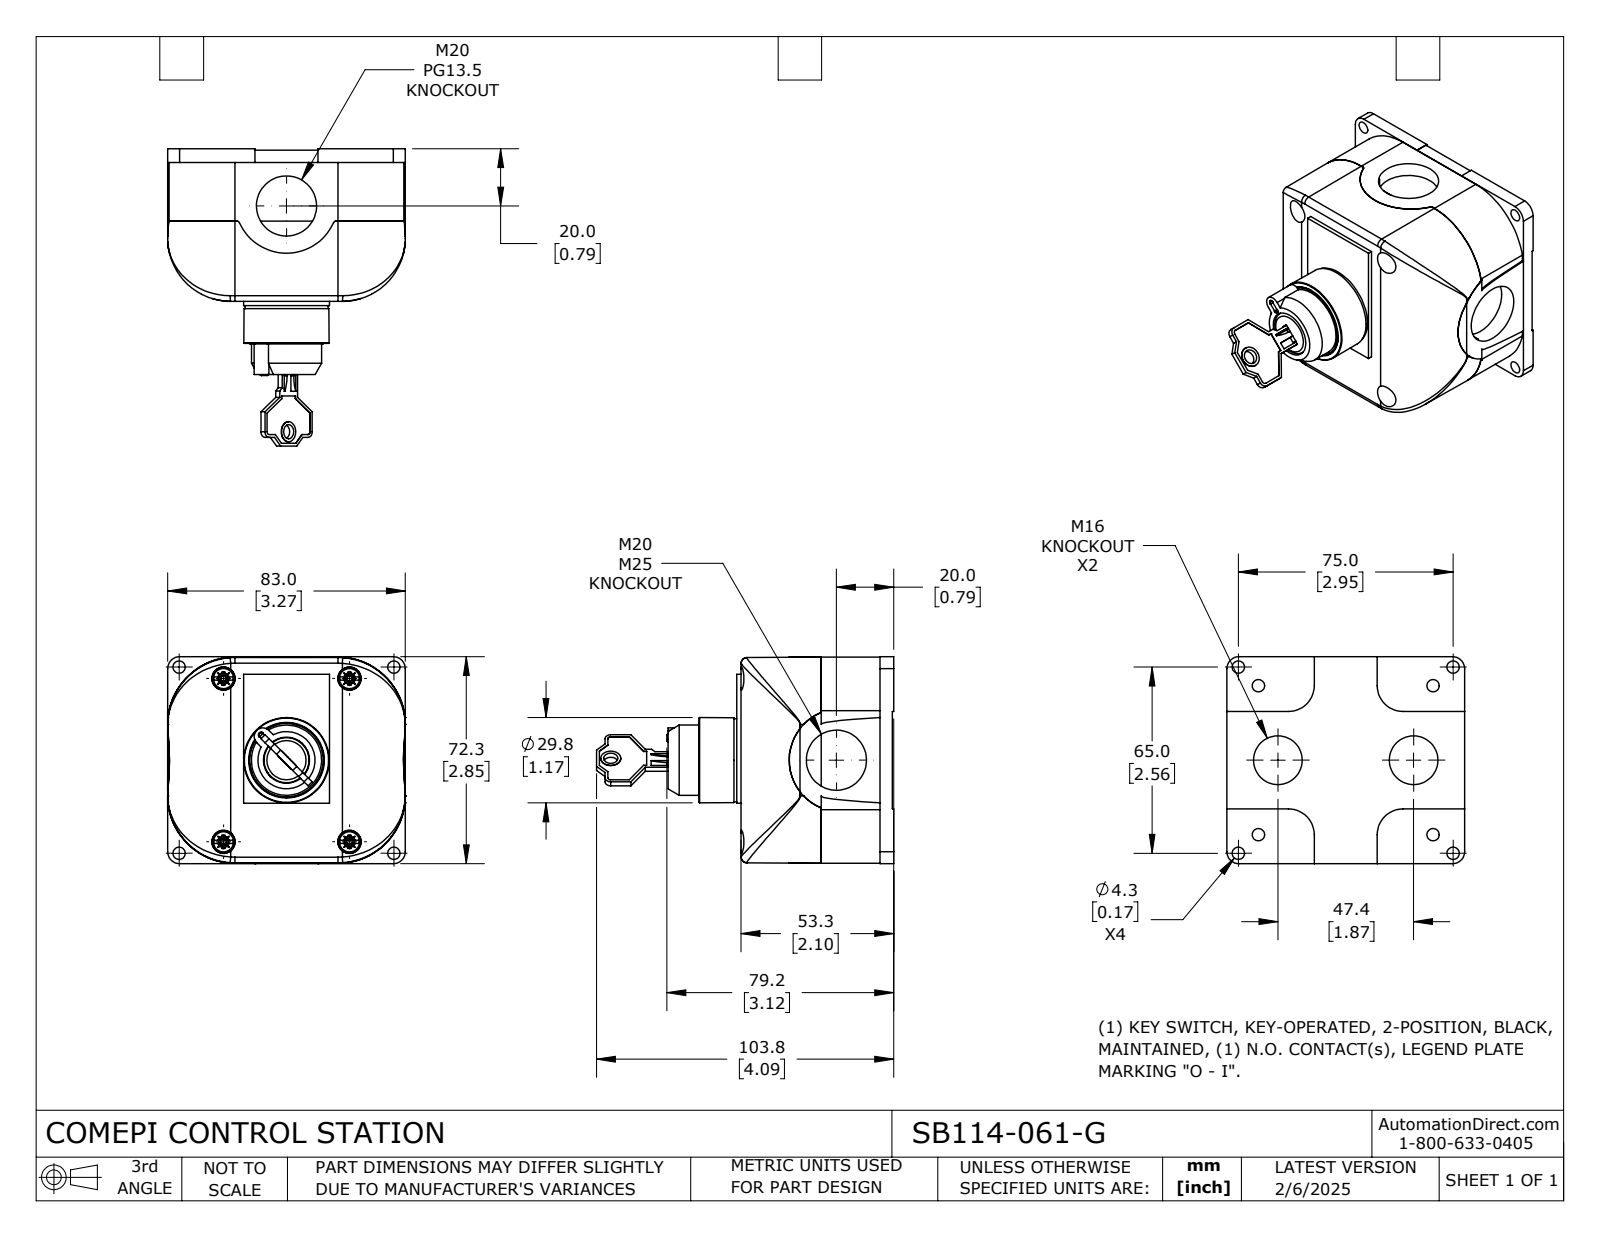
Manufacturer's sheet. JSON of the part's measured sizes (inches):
{"part_name": "SB114-061-G", "step_written_by": "SolidWorks 2024 (CONFIG_CONTROL_DESIGN)", "units": "inches", "bodies": {"solids": 5, "faces": 691, "planar": 409, "cylindrical": 183, "other": 99}, "overall_size": [4.087, 3.268, 2.846], "volume_in3": 13.19, "surface_area_in2": 98.02, "round_holes": [[0.169, 8], [0.323, 4], [0.669, 2], [0.827, 2], [0.094, 1], [0.197, 1], [0.5, 1], [0.634, 1], [0.75, 1], [0.752, 1], [0.854, 1], [0.886, 1]], "round_bosses_or_shafts": [[0.276, 5], [1.142, 1], [1.012, 1], [0.965, 1], [0.85, 1], [0.618, 1], [0.492, 1], [0.441, 1]], "partial_cylinders_radius": [[0.039, 8], [0.079, 6], [0.035, 4], [0.354, 4], [0.38, 4], [0.925, 4], [0.591, 3], [0.01, 2]], "face_to_face_distances": [2.079, 0.098, 0.976, 1.102, 0.878, 1.98, 0.118, 0.02, 0.996, 2.098], "hole_center_spacings": [0.376, 1.058, 1.39, 1.578, 1.954, 2.32, 2.367, 2.689]}
